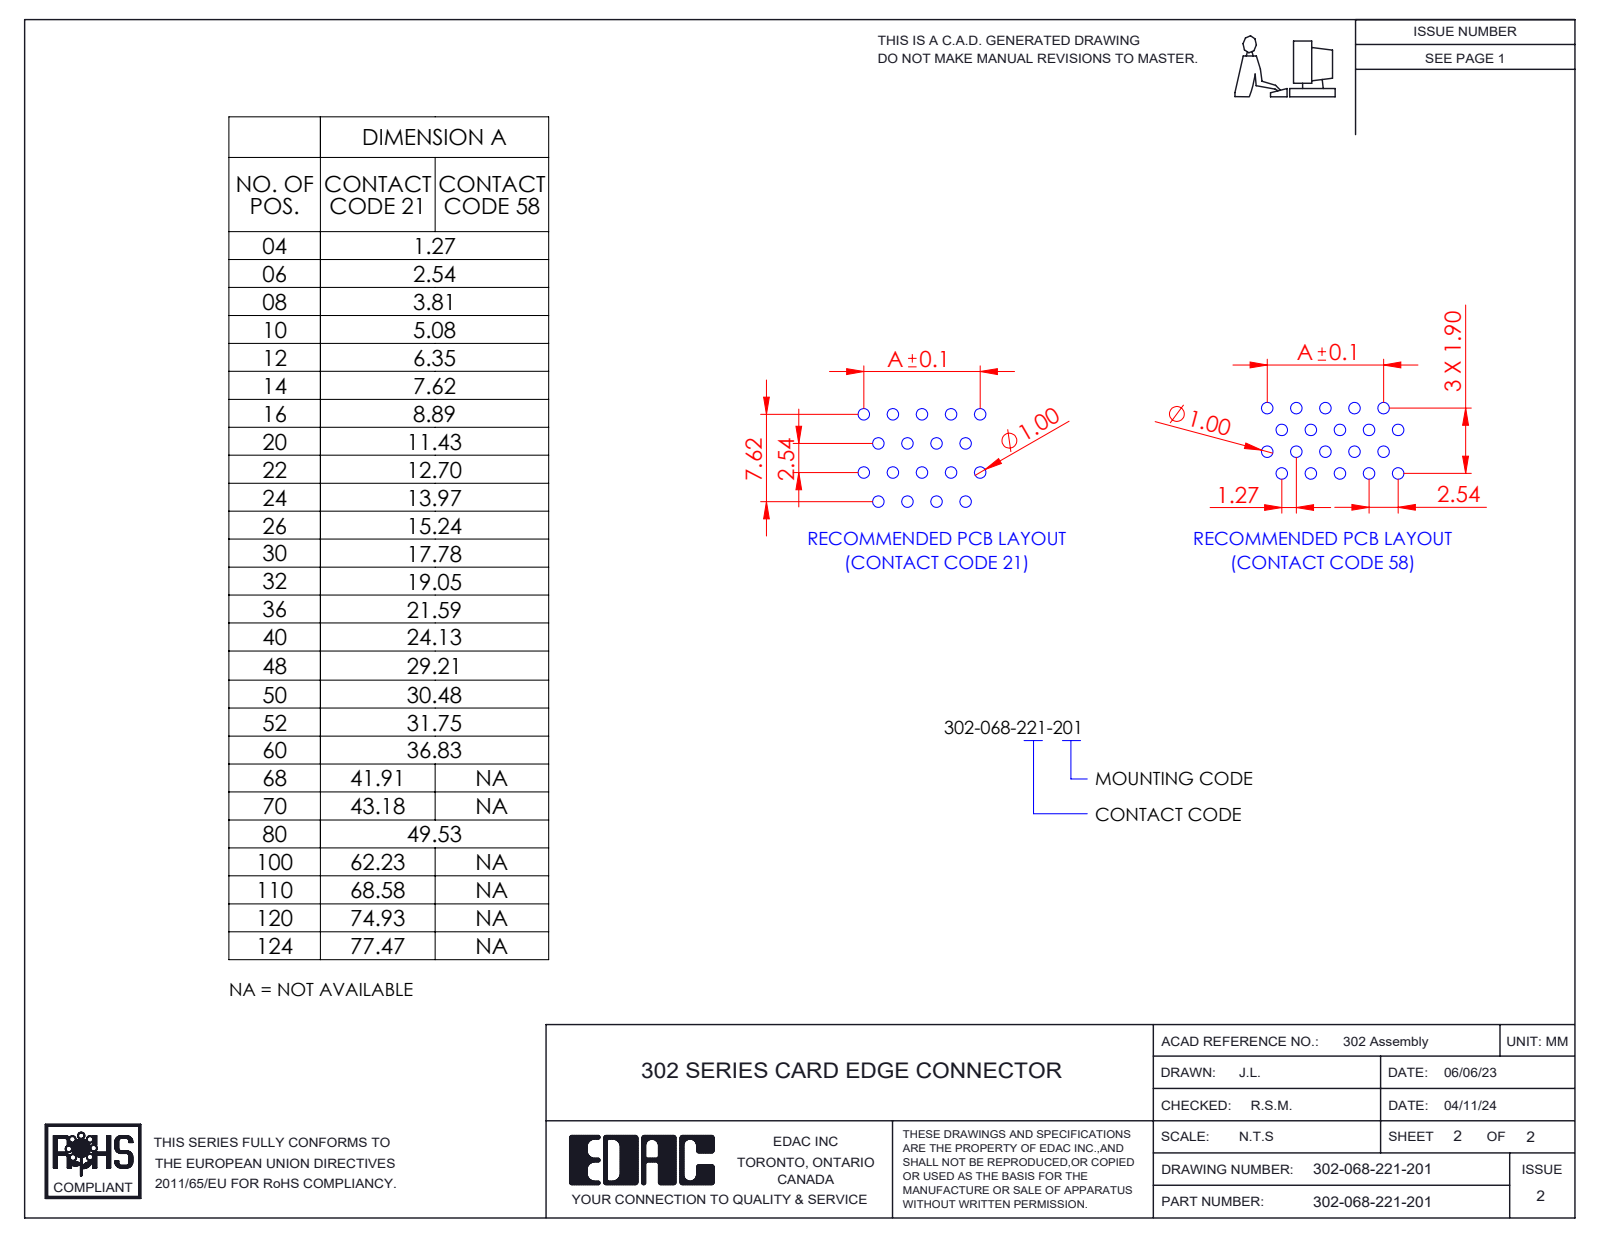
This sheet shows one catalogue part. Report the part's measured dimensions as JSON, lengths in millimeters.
{"part_name": "302-068-221-201; Contact_302-290-X21 (2); Contact_302-290-X21 (1); HSG_Vertical HSG", "step_written_by": "SolidWorks 2023 (CONFIG_CONTROL_DESIGN)", "units": "millimeters", "bodies": {"solids": 69, "faces": 3160, "planar": 2327, "cylindrical": 693, "other": 140}, "overall_size": [49.28, 17.63, 8.88], "volume_mm3": 3836, "surface_area_mm2": 10460, "partial_cylinders_radius": [[0.2, 76], [2.03, 4], [2.09, 4], [0.11, 2], [0.4, 2], [0.41, 2], [1.25, 2], [1.53, 2]], "face_to_face_distances": [2.54, 1.27, 5.08, 3.81, 7.62, 6.35, 8.88, 8.89, 10.16, 11.43]}
